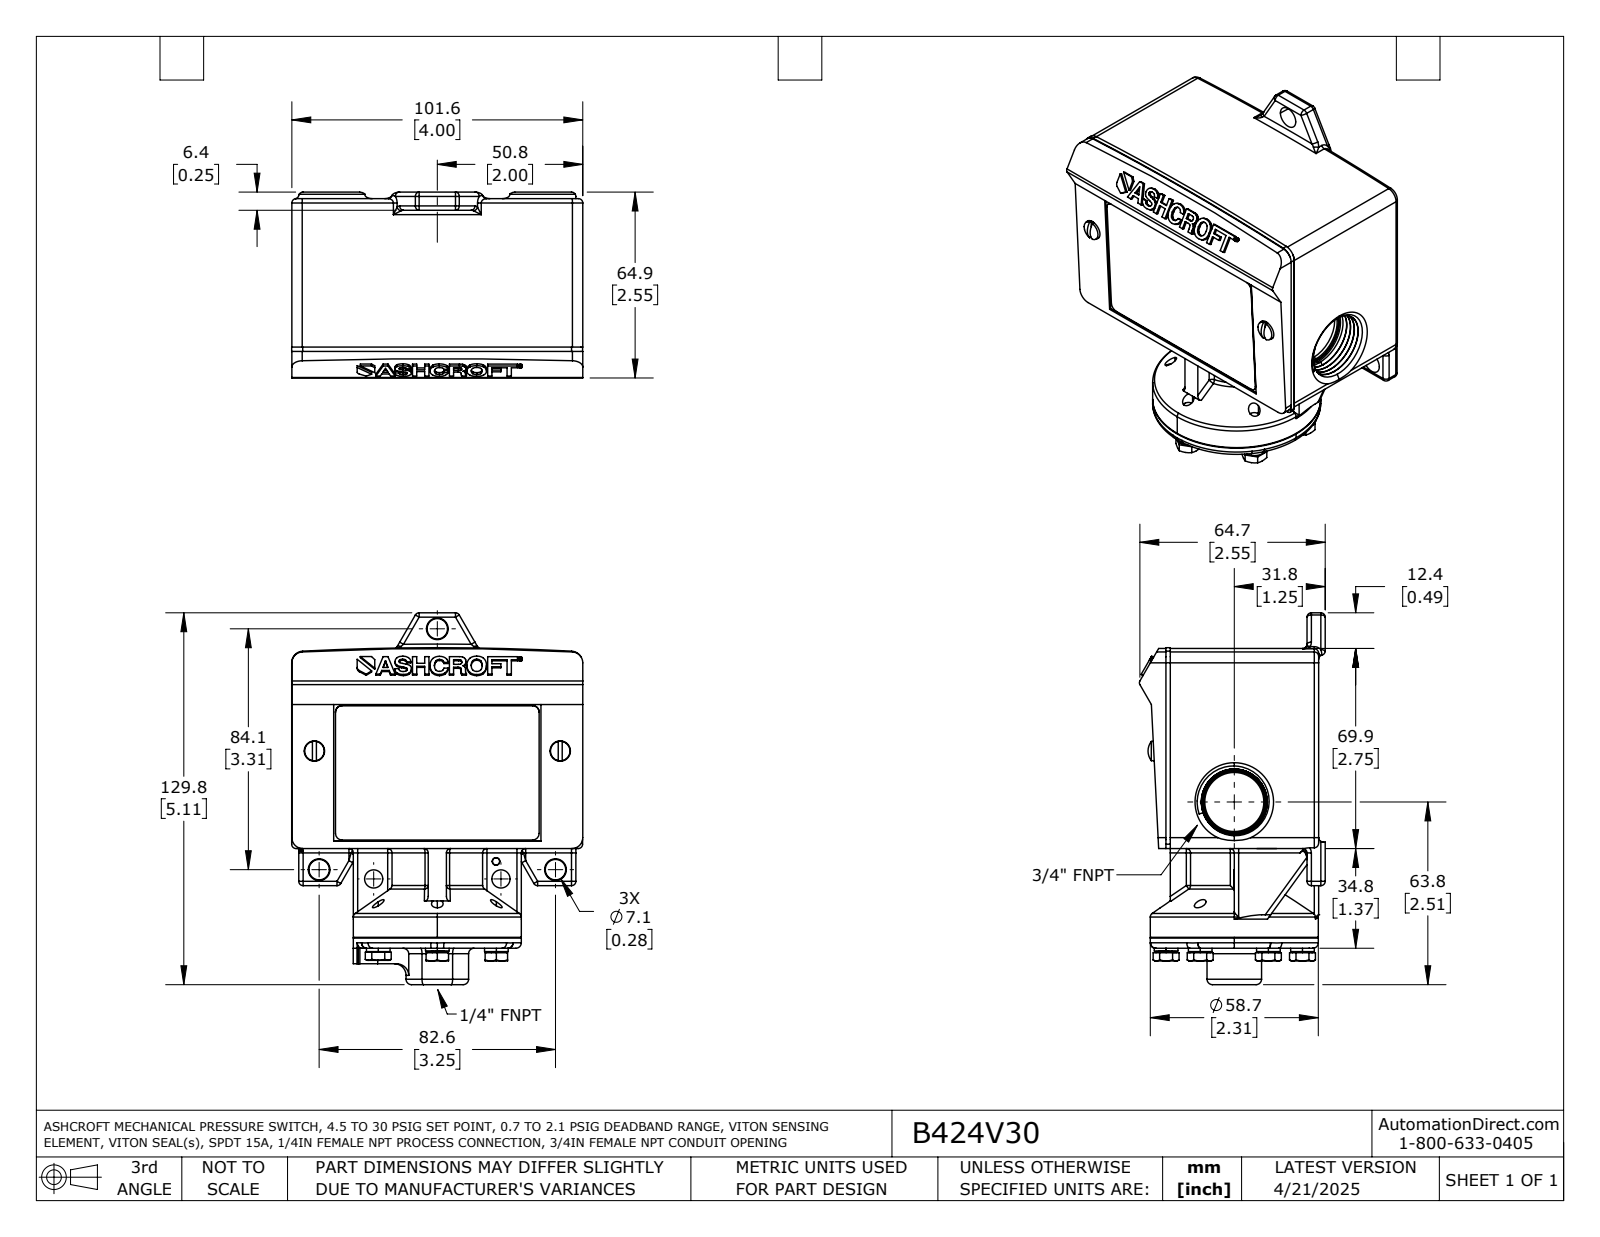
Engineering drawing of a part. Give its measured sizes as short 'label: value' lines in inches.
name: B424V30
written by: SolidWorks 2021 (AUTOMOTIVE_DESIGN)
unit: in
bodies: 2 solids, 1259 faces (345 planar, 472 cylindrical, 442 other)
size: 5.111 × 4.003 × 2.555
volume: 28.57 in³; area: 84.51 in²
holes: 6× ⌀0.161, 5× ⌀0.192, 5× ⌀0.209, 4× ⌀0.187, 2× ⌀0.28, 1× ⌀0.455, 1× ⌀0.812
bosses: 6× ⌀0.325, 6× ⌀0.278, 5× ⌀0.19, 2× ⌀0.27, 2× ⌀0.25, 1× ⌀2.31
rounds: 92× R0.06, 5× R0.03, 4× R0.075, 4× R0.09, 4× R0.15, 2× R0.01, 2× R0.094, 2× R0.16
face distances: 4, 0.015, 1.37, 0.09, 3.91, 0.44, 3.56, 3.47, 0.35, 0.845
hole spacings: 0.937, 1.624, 1.875, 0.938, 3.38
